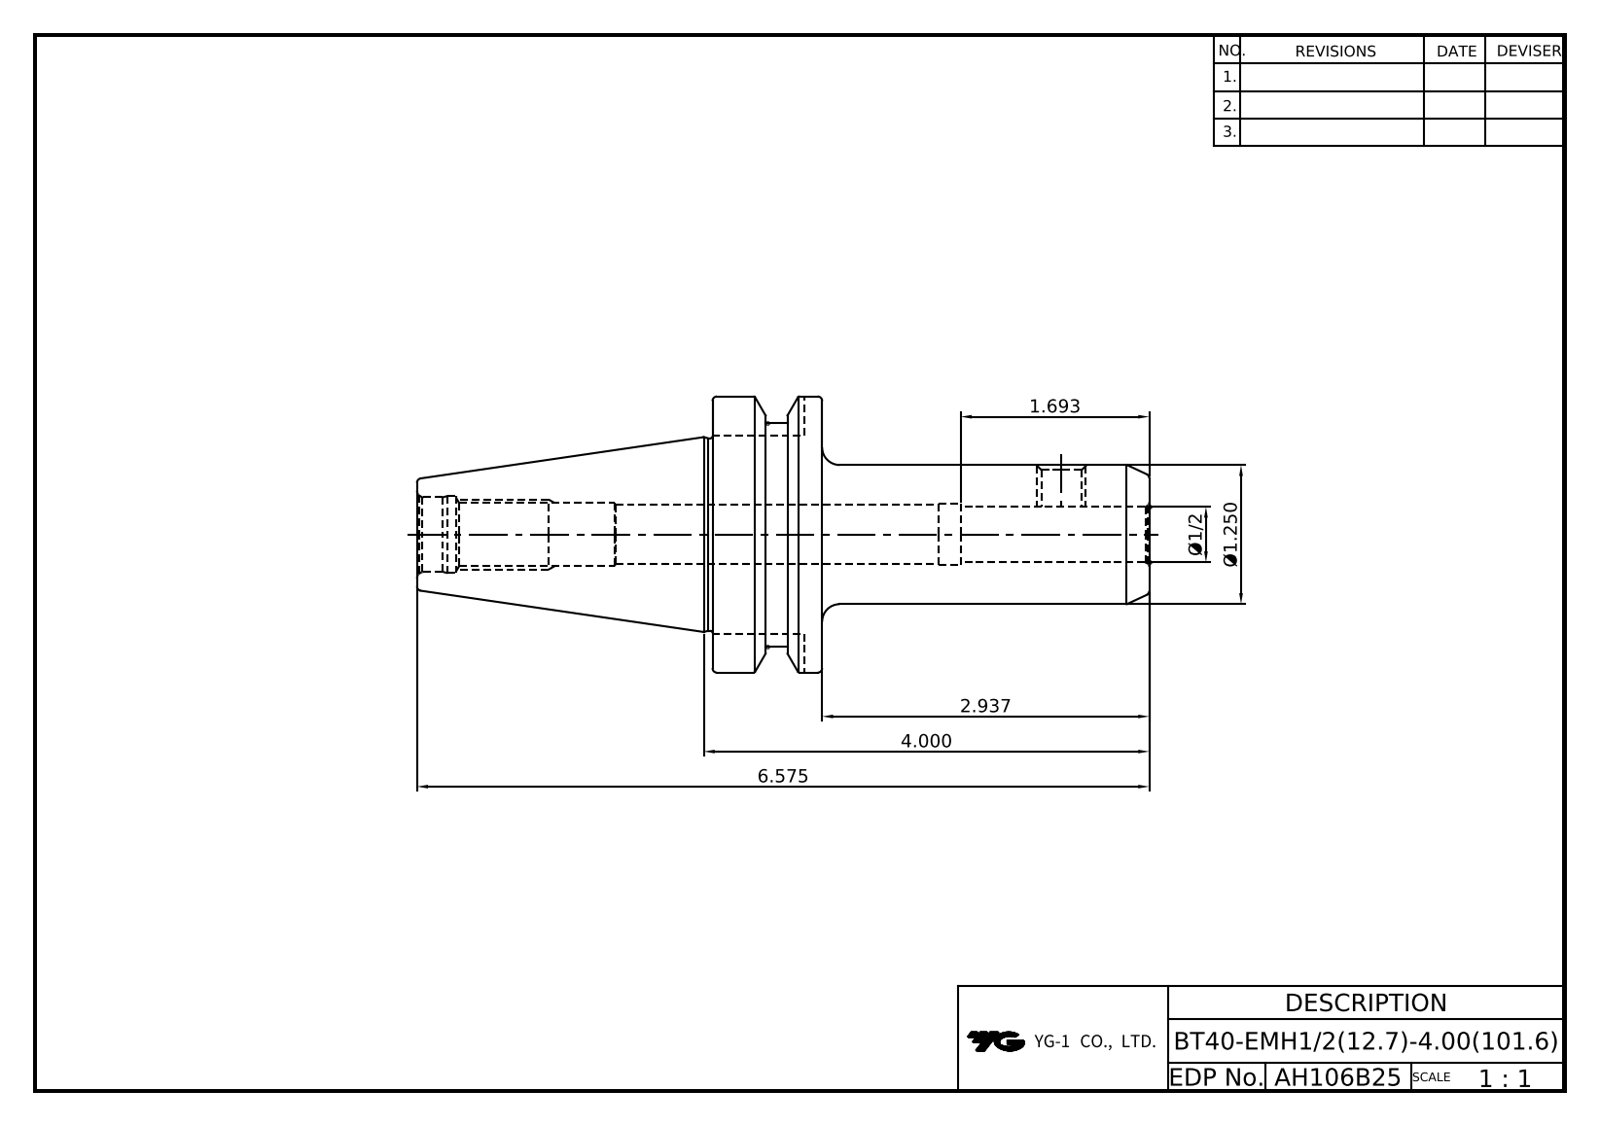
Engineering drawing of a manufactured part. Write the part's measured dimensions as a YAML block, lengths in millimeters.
part_name: "BT40-EMH12.7-101.6"
step_written_by: "Autodesk Inventor 2022 (AUTOMOTIVE_DESIGN)"
units: millimeters
bodies: {solids: 1, faces: 52, planar: 17, cylindrical: 16, other: 19}
overall_size: [167, 63, 63]
volume: 167866
surface_area: 32721
round_holes:
  - {diameter: 9.73, count: 1}
  - {diameter: 12.7, count: 1}
  - {diameter: 13.5, count: 1}
  - {diameter: 13.84, count: 1}
  - {diameter: 13.9, count: 1}
  - {diameter: 17, count: 1}
  - {diameter: 17.6, count: 1}
round_bosses_or_shafts:
  - {diameter: 63, count: 1}
  - {diameter: 52.6, count: 1}
  - {diameter: 44, count: 1}
  - {diameter: 31.75, count: 1}
partial_cylinders:
  - {radius: 8.05, count: 1}
face_to_face_distances: [25, 99.6, 74.6, 45.2, 16.1, 67.4, 92.4, 167, 5, 84.5]
